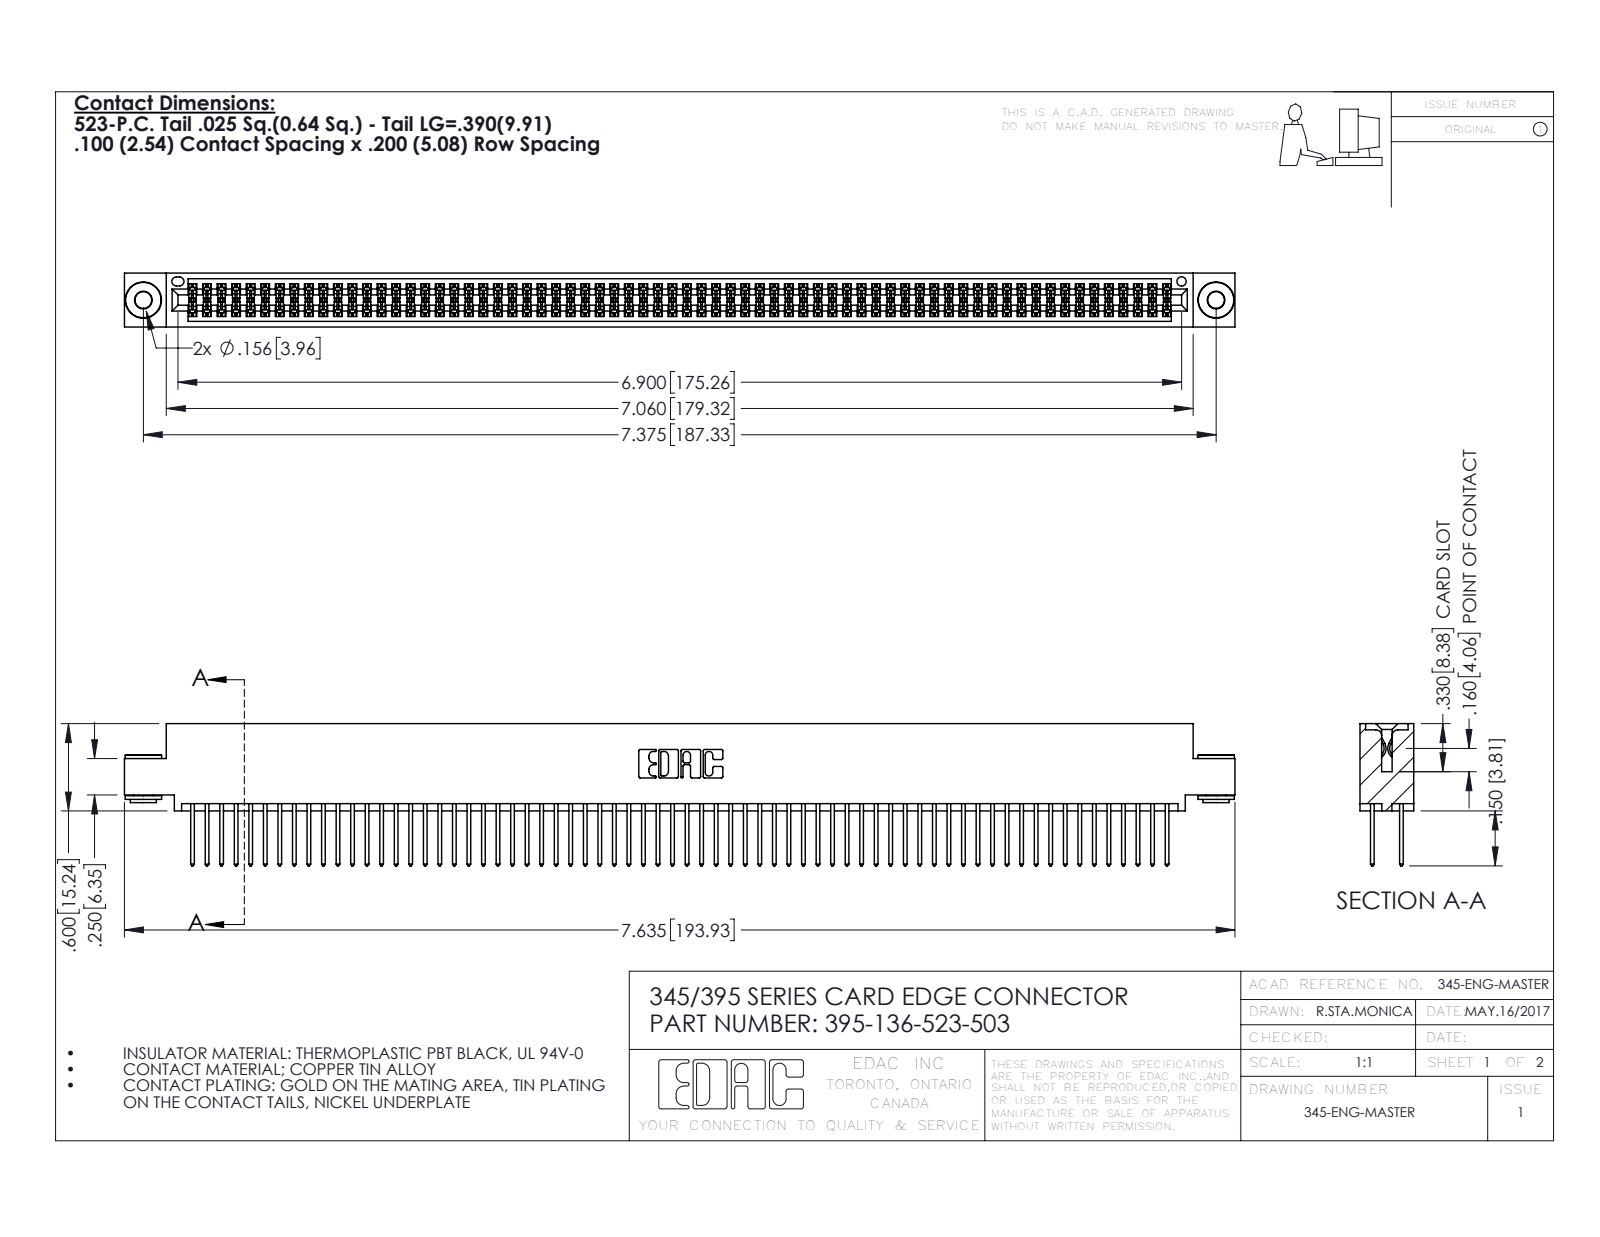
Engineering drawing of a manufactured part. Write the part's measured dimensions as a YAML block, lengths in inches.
part_name: "395-136-523-503; 345-292-001_345-293-123; 345-250-002_345-250-002-102; 345 Part_0.110 Offset - 0.156 Dia-TH"
step_written_by: "SolidWorks 2016 (CONFIG_CONTROL_DESIGN)"
units: inches
bodies: {solids: 139, faces: 6968, planar: 4582, cylindrical: 2378, other: 8}
overall_size: [7.635, 0.977, 0.37]
volume: 1.178
surface_area: 47.41
round_holes:
  - {diameter: 0.116, count: 2}
  - {diameter: 0.156, count: 2}
  - {diameter: 0.064, count: 1}
round_bosses_or_shafts:
  - {diameter: 0.25, count: 2}
  - {diameter: 0.18, count: 2}
  - {diameter: 0.136, count: 2}
partial_cylinders:
  - {radius: 0.006, count: 204}
  - {radius: 0.01, count: 136}
  - {radius: 0.01, count: 22}
  - {radius: 0.007, count: 6}
  - {radius: 0.031, count: 6}
  - {radius: 0.026, count: 3}
  - {radius: 0.014, count: 2}
  - {radius: 0.019, count: 2}
face_to_face_distances: [0.072, 0.298, 0.2, 0.025, 0.098, 0.272, 0.37, 0.225, 0.175, 0.149]
hole_center_spacings: [0.27, 7.139, 7.375]
